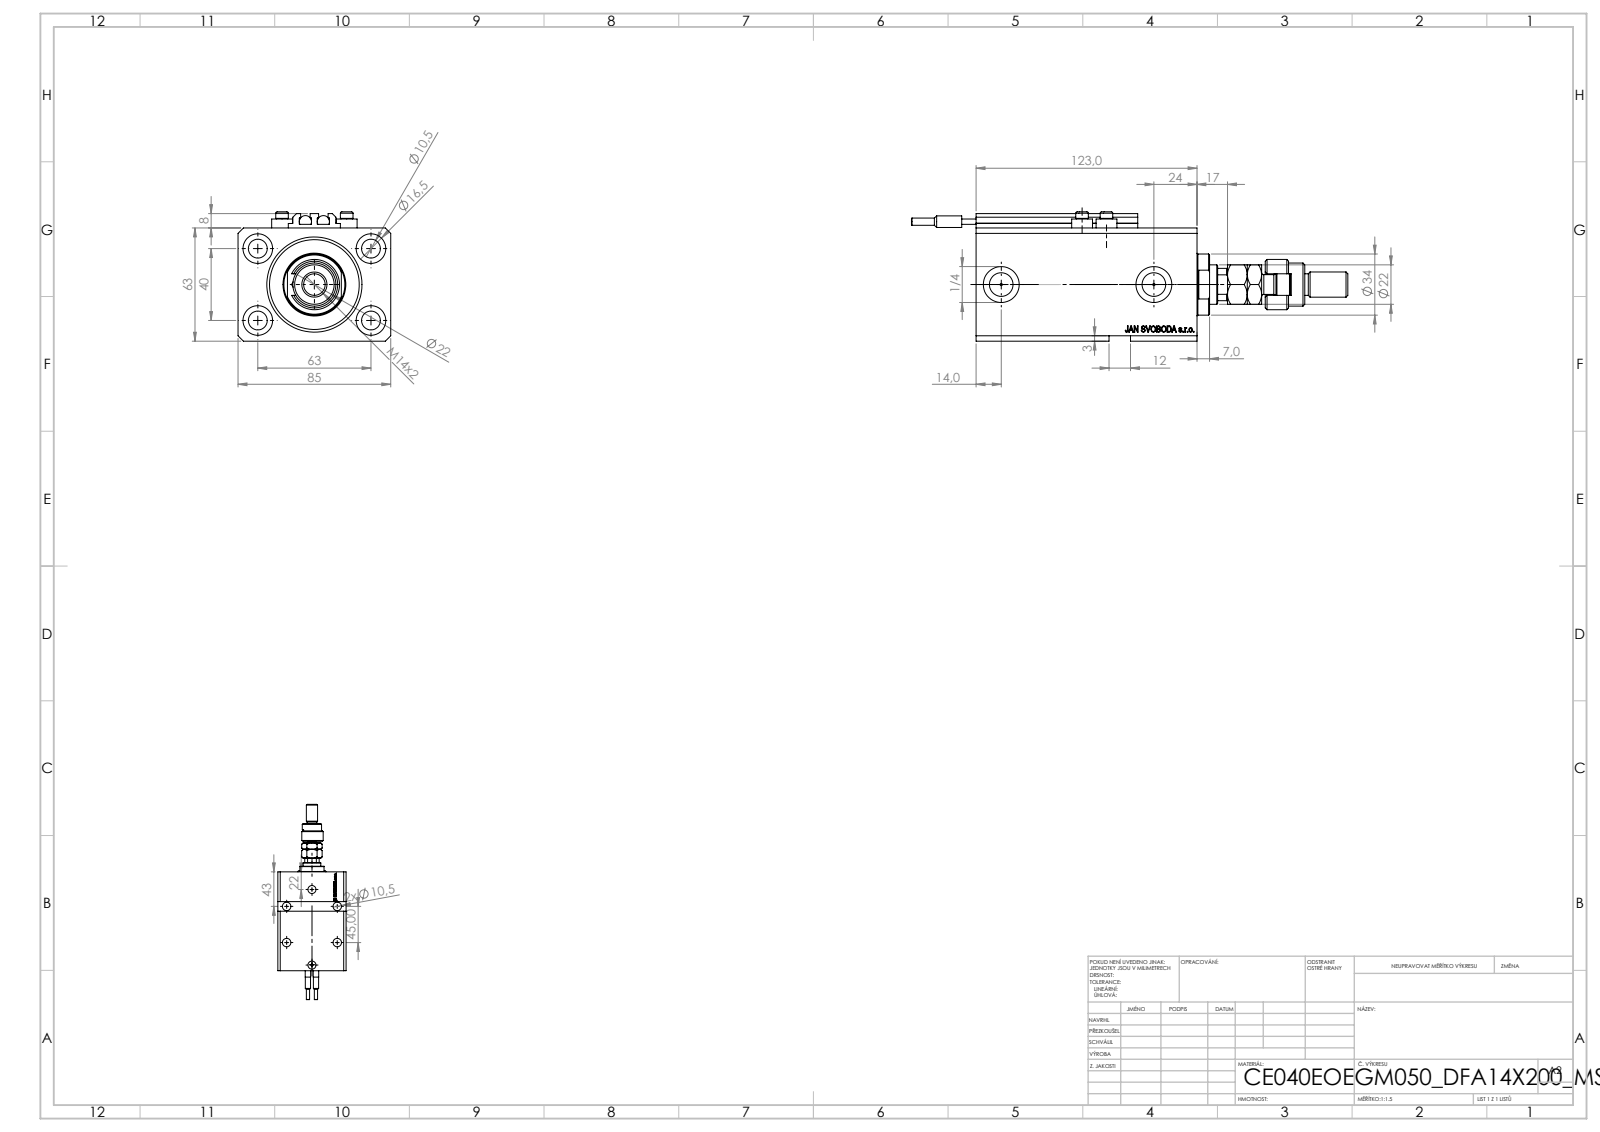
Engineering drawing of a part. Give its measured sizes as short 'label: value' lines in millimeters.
name: V250CE_C_VCP; SWITCH_V250CE; V250CE_E_Body; ALLEN BOLT V250CE (+3 more)
written by: SolidWorks 2019 (CONFIG_CONTROL_DESIGN)
unit: mm
bodies: 12 solids, 1244 faces (595 planar, 171 cylindrical, 478 other)
size: 243 × 85 × 72
volume: 582 126 mm³; area: 130 039 mm²
holes: 8× ⌀10.5, 4× ⌀1.25, 4× ⌀4, 4× ⌀16.5, 2× ⌀10, 2× ⌀13.16, 2× ⌀20, 1× ⌀12.5, 1× ⌀22, 1× ⌀40, 1× ⌀53
bosses: 4× ⌀11.6, 4× ⌀7, 2× ⌀6.8, 2× ⌀6.5, 2× ⌀4, 1× ⌀34, 1× ⌀28, 1× ⌀24
rounds: 10× R0.2, 1× R9.75, 1× R10.5
face distances: 63, 85, 17, 123, 106, 3, 11.4, 94.6, 111.6, 65
hole spacings: 37.31, 63, 13.6, 15.4, 24.96, 27.54, 33.62, 36
